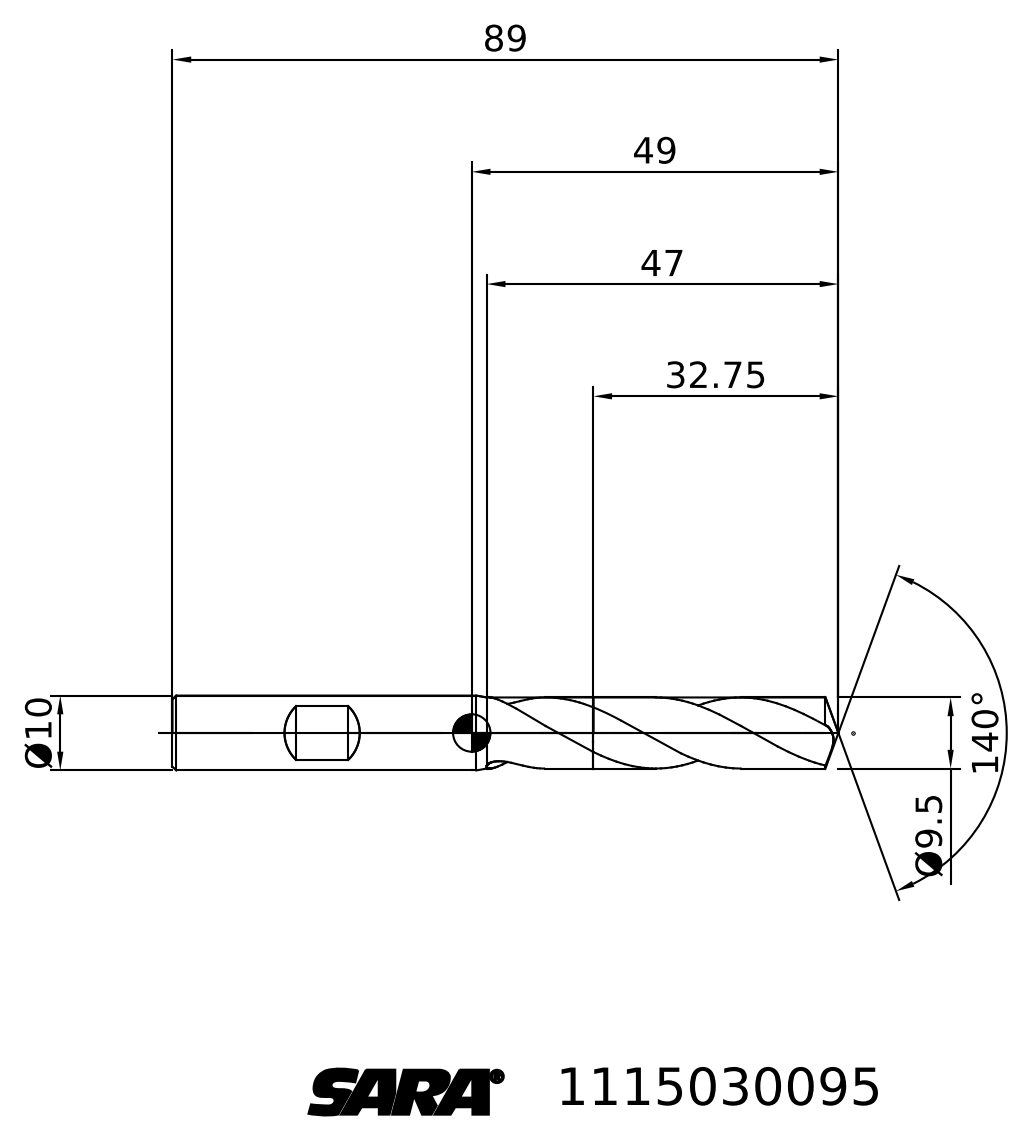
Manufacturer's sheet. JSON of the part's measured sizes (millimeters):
{"step_written_by": "TDM (AUTOMOTIVE_DESIGN)", "units": "millimeters", "bodies": {"solids": 2, "faces": 30, "planar": 6, "cylindrical": 0, "other": 24}, "overall_size": [89, 20.49, 10], "volume_mm3": 5433, "surface_area_mm2": 3010, "face_to_face_distances": [56.25]}
